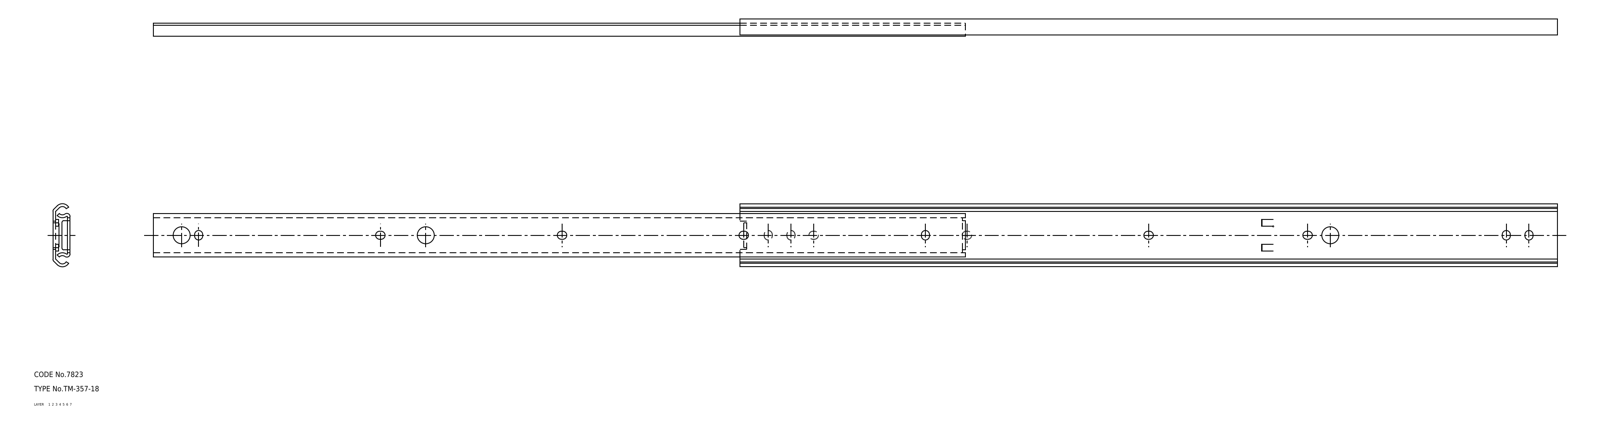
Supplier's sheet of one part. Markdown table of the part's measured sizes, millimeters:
| quantity | value |
| --- | --- |
| part name | member_B; member_A; TM_357_18 |
| STEP written by | SolidWorks 2015 (AUTOMOTIVE_DESIGN) |
| units | millimeters |
| bodies | 2 solids, 121 faces (62 planar, 59 cylindrical, 0 other) |
| overall size | 785.2 × 35.3 × 9.6 |
| volume | 57 622 mm³ |
| surface area | 75 709 mm² |
| round holes (diameter × count) | 9.5 × 3 |
| partial cylindrical surfaces (radius × count) | 2.25 × 26, 1 × 4, 1.6 × 4, 0.2 × 2, 1.8 × 2, 2.4 × 2, 2.5 × 2, 4 × 2 |
| main face-to-face distances | 1.6, 8, 9.6, 6.4, 331, 4.5, 122.4, 454.2, 785.2, 452.6 |
| hole center spacings | 136.5, 505.8, 642.3 |
